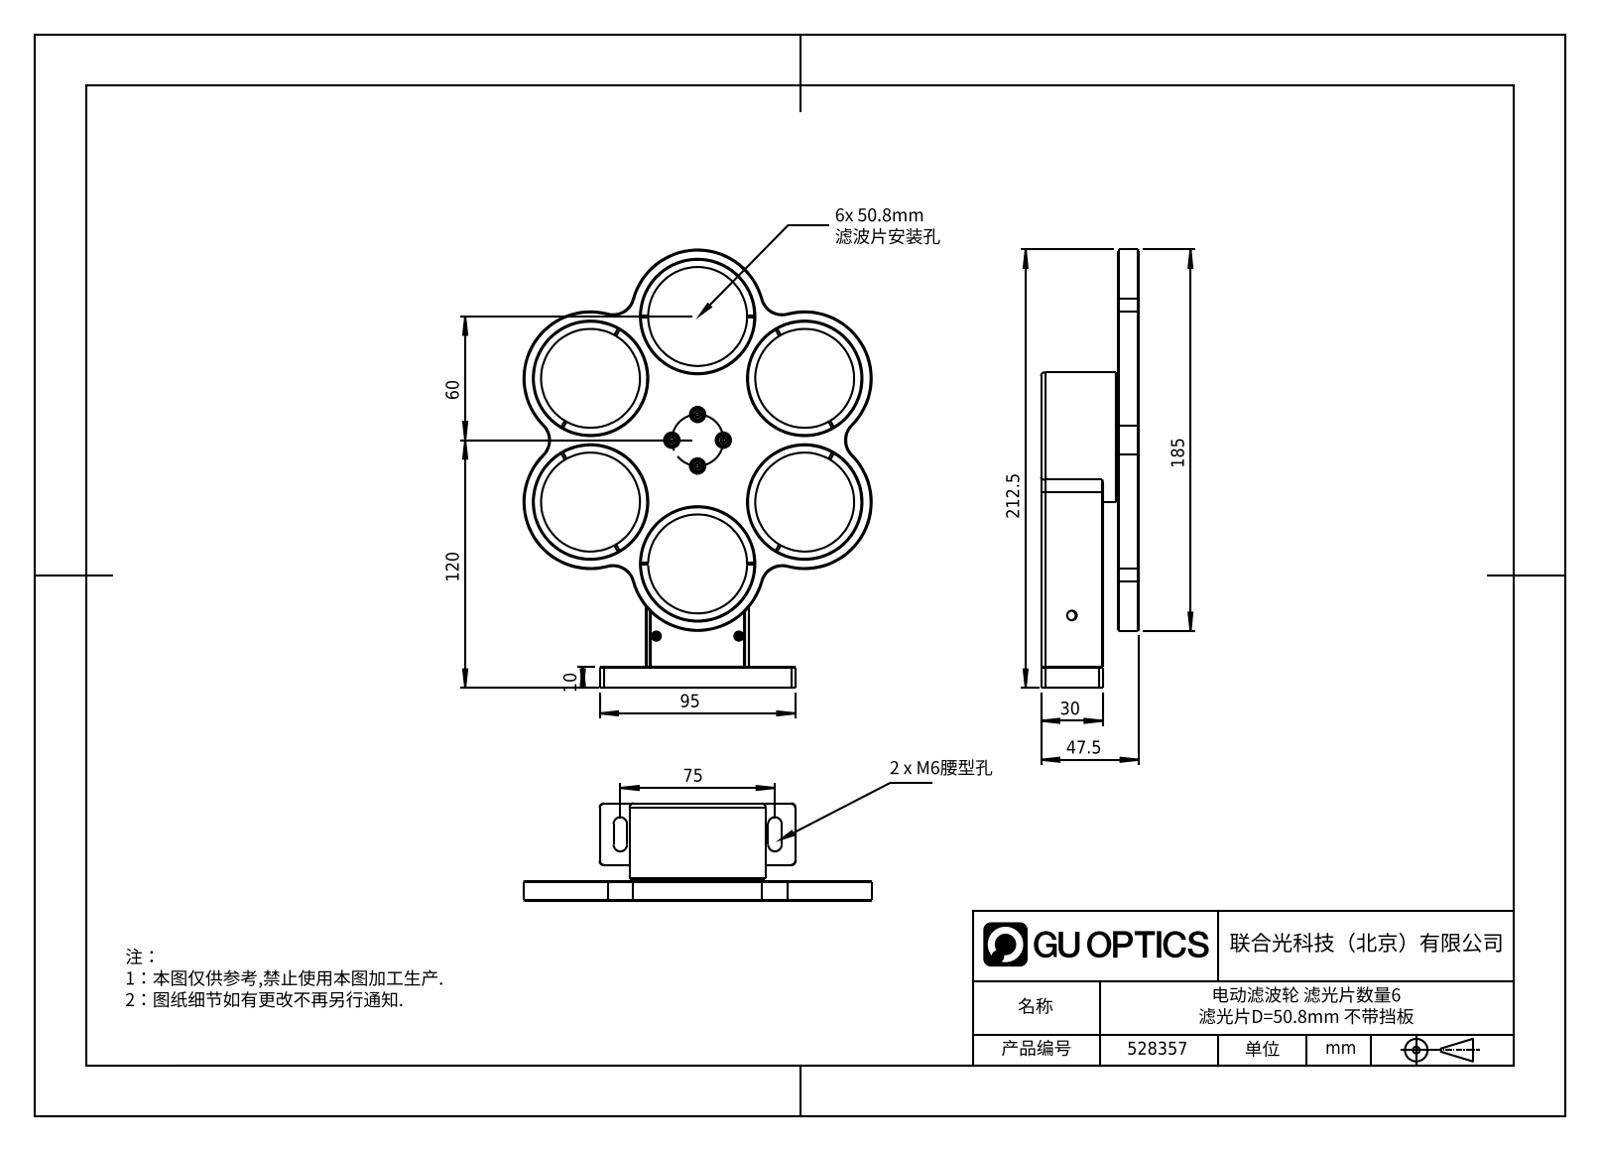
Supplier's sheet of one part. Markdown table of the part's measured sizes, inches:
| quantity | value |
| --- | --- |
| part name | 528357 |
| STEP written by | SolidWorks 2020 (CONFIG_CONTROL_DESIGN) |
| units | inches |
| bodies | 0 solids, 341 faces (189 planar, 58 cylindrical, 94 other) |
| overall size | 8.366 × 6.65 × 1.87 |
| round holes (diameter × count) | 1.89 × 6, 0.315 × 4, 2.598 × 1 |
| round bosses / shafts (diameter × count) | 0.256 × 8, 2.165 × 2, 0.276 × 2, 0.217 × 2, 0.173 × 2, 0.185 × 1 |
| partial cylindrical surfaces (radius × count) | 0.394 × 8, 0.079 × 6, 1.28 × 6, 0.13 × 4 |
| main face-to-face distances | 0.197, 0.394, 0.354, 0.157, 0.039, 0.236, 1.476, 1.516, 1.713, 1.87 |
| hole center spacings | 2.362, 4.091, 4.724, 0.709, 1.654, 1.799 |
